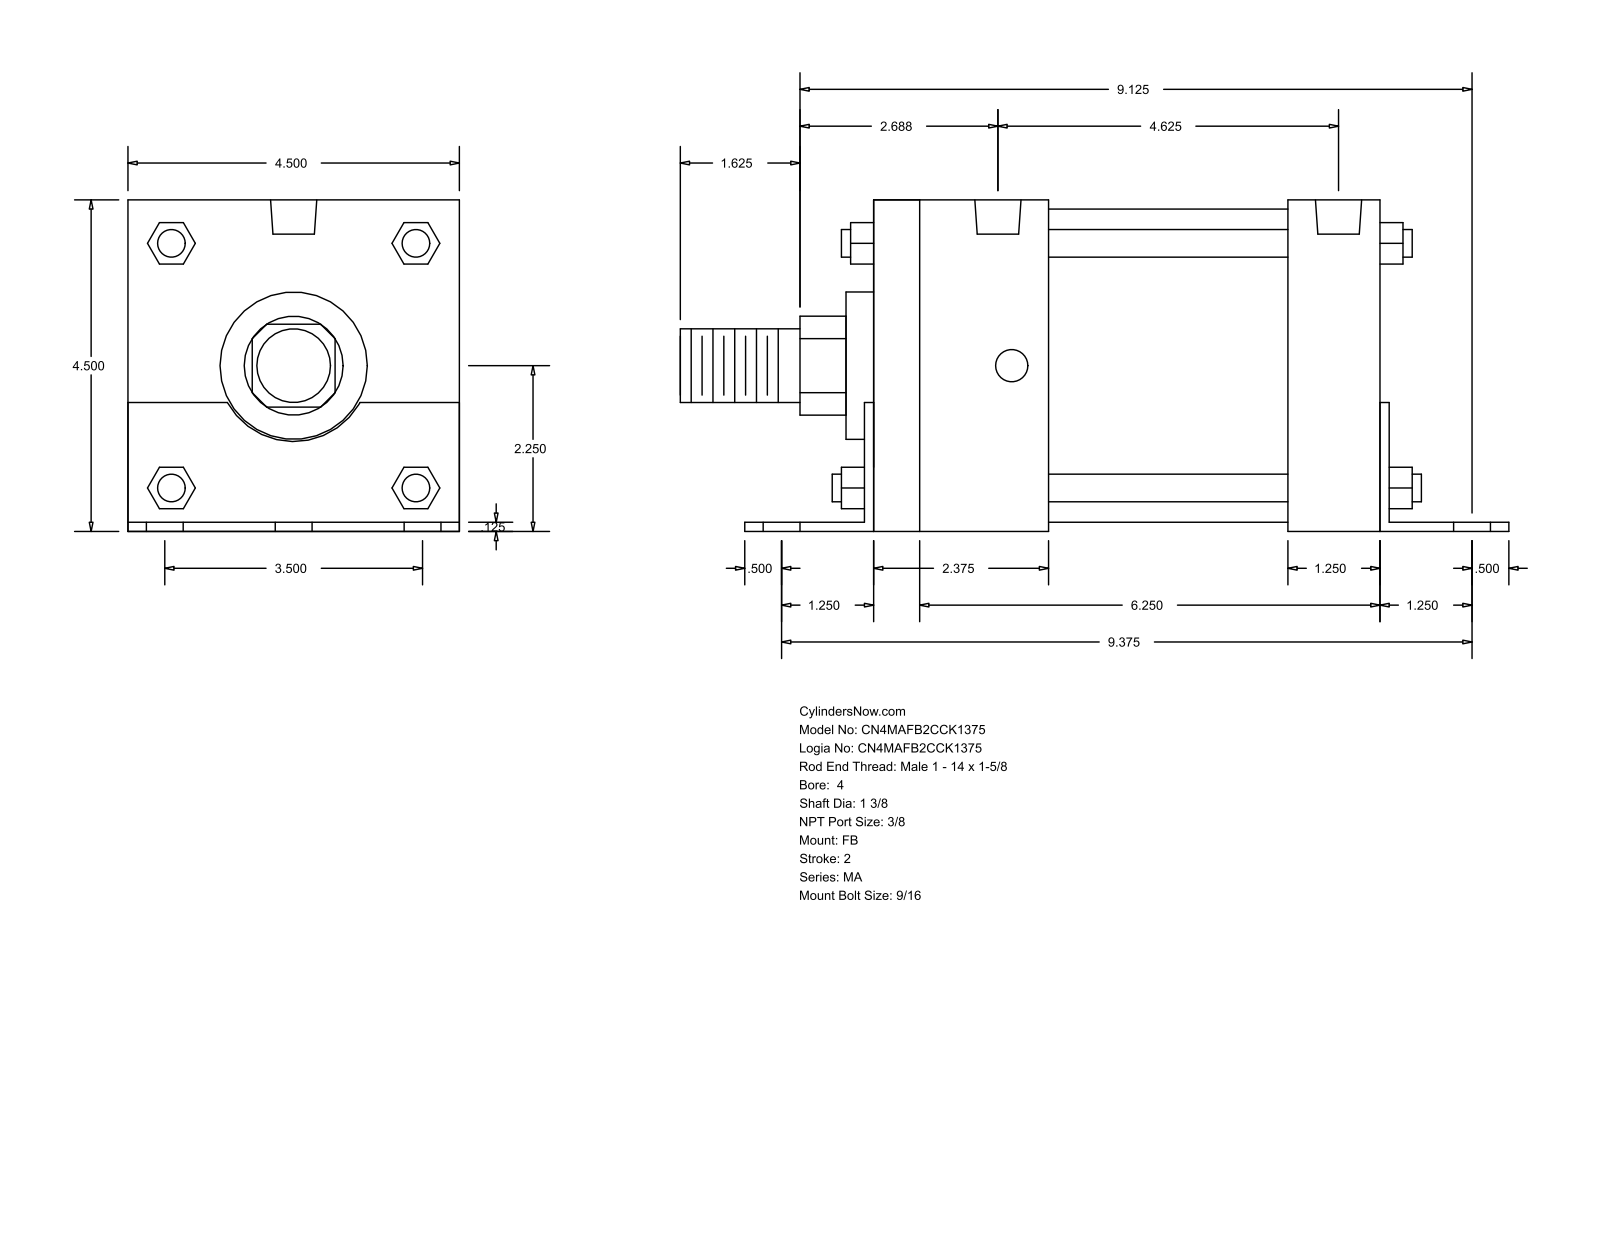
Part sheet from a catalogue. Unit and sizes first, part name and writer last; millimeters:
Units: millimetres
Overall size (bounding box): 285.75 × 114.35 × 114.3
Round holes (diameter × count): ⌀14.29 ×6, ⌀11.11 ×4, ⌀15.93 ×2
Round bosses / shafts (diameter × count): ⌀9.53 ×4, ⌀107.95 ×1, ⌀50.8 ×1, ⌀34.92 ×1, ⌀25.4 ×1
Partial cylindrical surfaces — rounded edges, fillets, slot ends (radius × count): R17.06 ×1, R26.16 ×1
Main face-to-face distances: 114.3, 3.17, 114.35, 3.12, 111.18, 177.8, 174.63, 180.97, 31.75, 146.05
Hole centre spacings: 44.45, 242.24, 238.13, 4.77, 64, 67.51, 86.85, 88.9
Bodies: 0 solids, 140 faces (105 planar, 35 cylindrical, 0 other)
Part name (STEP PRODUCT): MA_FB__0400_1.375
STEP written by: GSSL Pune (CONFIG_CONTROL_DESIGN)
